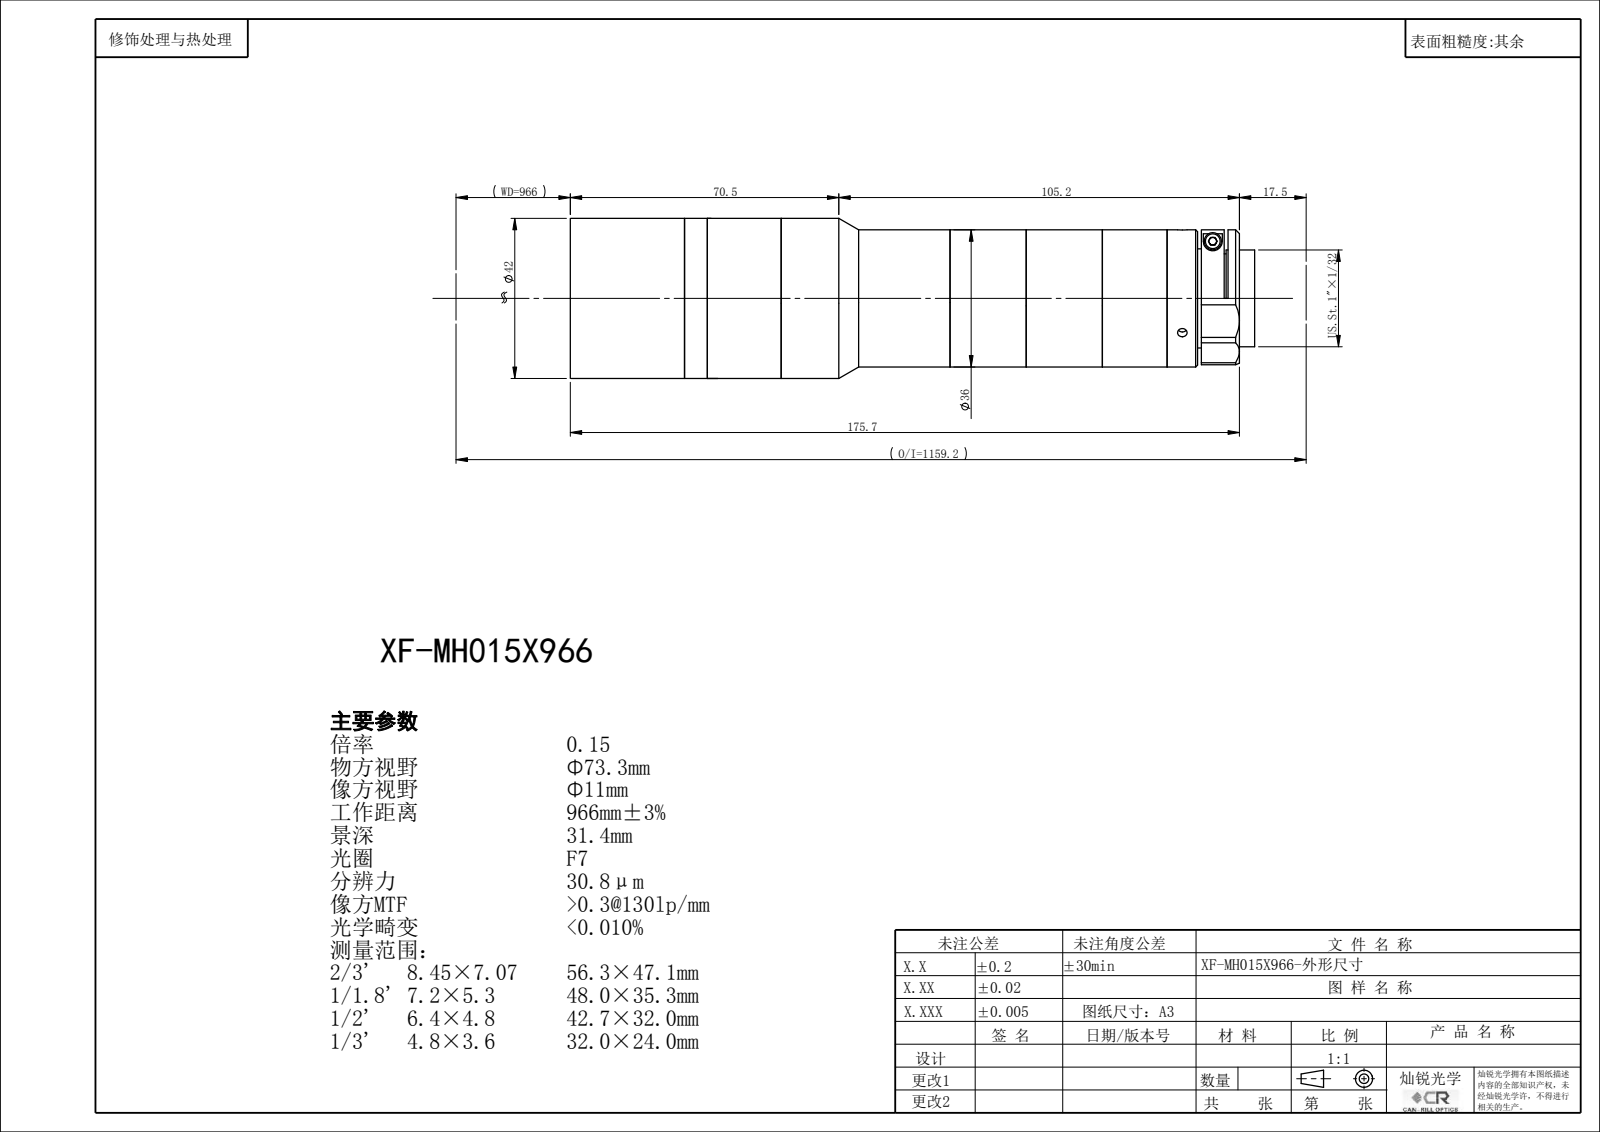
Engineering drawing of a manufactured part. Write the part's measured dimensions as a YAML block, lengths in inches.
part_name: "XF-MH015X966"
step_written_by: "SolidWorks 2022 (CONFIG_CONTROL_DESIGN)"
units: inches
bodies: {solids: 0, faces: 136, planar: 70, cylindrical: 44, other: 22}
overall_size: [7.098, 1.654, 1.654]
round_holes:
  - {diameter: 0.098, count: 3}
  - {diameter: 0.882, count: 1}
  - {diameter: 0.945, count: 1}
  - {diameter: 1.039, count: 1}
  - {diameter: 1.299, count: 1}
  - {diameter: 1.433, count: 1}
round_bosses_or_shafts:
  - {diameter: 1.654, count: 1}
  - {diameter: 1.417, count: 1}
  - {diameter: 1.339, count: 1}
  - {diameter: 1, count: 1}
face_to_face_distances: [0.787, 0.771, 0.059, 0.712, 6.17, 6.882, 6.941, 0.669, 5.501, 1.381]
